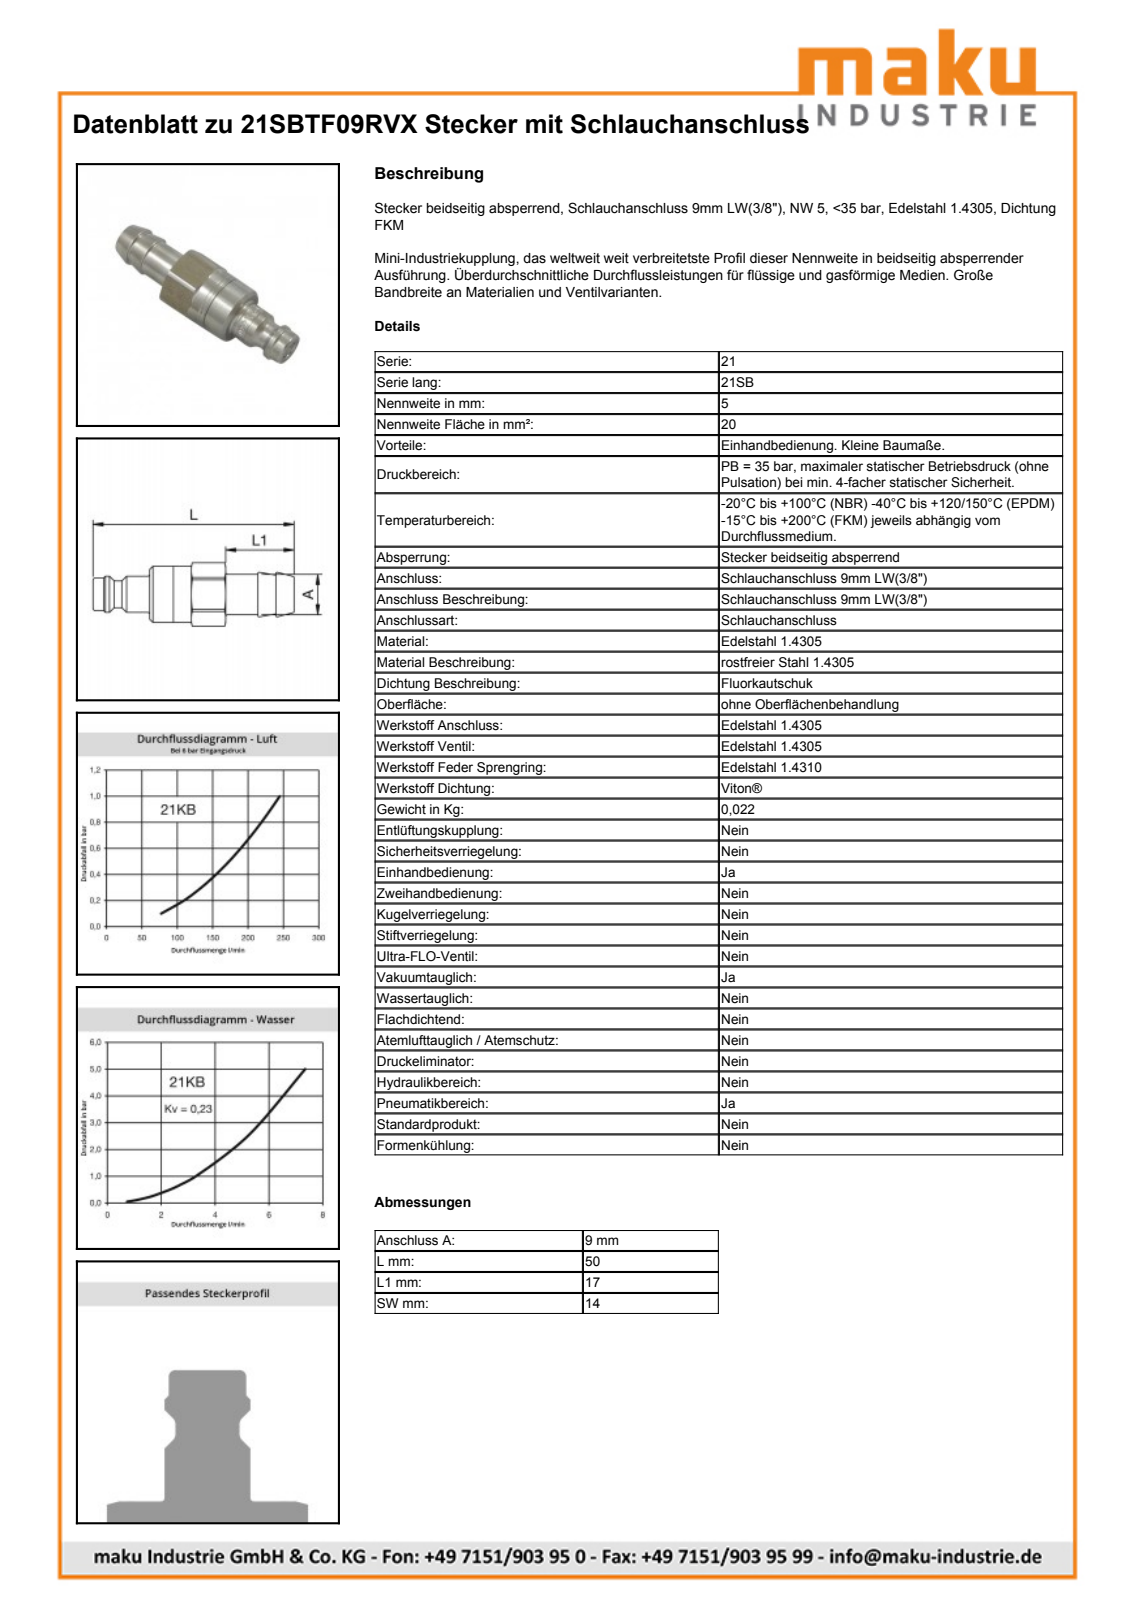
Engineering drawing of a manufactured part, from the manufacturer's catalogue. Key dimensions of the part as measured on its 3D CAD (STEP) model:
Part name (STEP PRODUCT): D111907
STEP written by: Autodesk Inventor 2013 (AUTOMOTIVE_DESIGN)
Units: millimetres
Bodies: 1 solid, 67 faces (14 planar, 18 cylindrical, 35 other)
Overall size (bounding box): 50 × 15.8 × 14
Volume: 4 407 mm³ · Surface area: 3 370 mm²
Round holes (diameter × count): ⌀5.5 ×1, ⌀9.5 ×1, ⌀10.45 ×1, ⌀12 ×1
Round bosses / shafts (diameter × count): ⌀14 ×1, ⌀11.98 ×1, ⌀11 ×1, ⌀9.05 ×1, ⌀9 ×1, ⌀8.1 ×1, ⌀6.65 ×1
Partial cylindrical surfaces — rounded edges, fillets, slot ends (radius × count): R7.9 ×1
Main face-to-face distances: 14, 17, 18.9, 35.9, 16.9, 2, 19, 9, 14.1, 31
